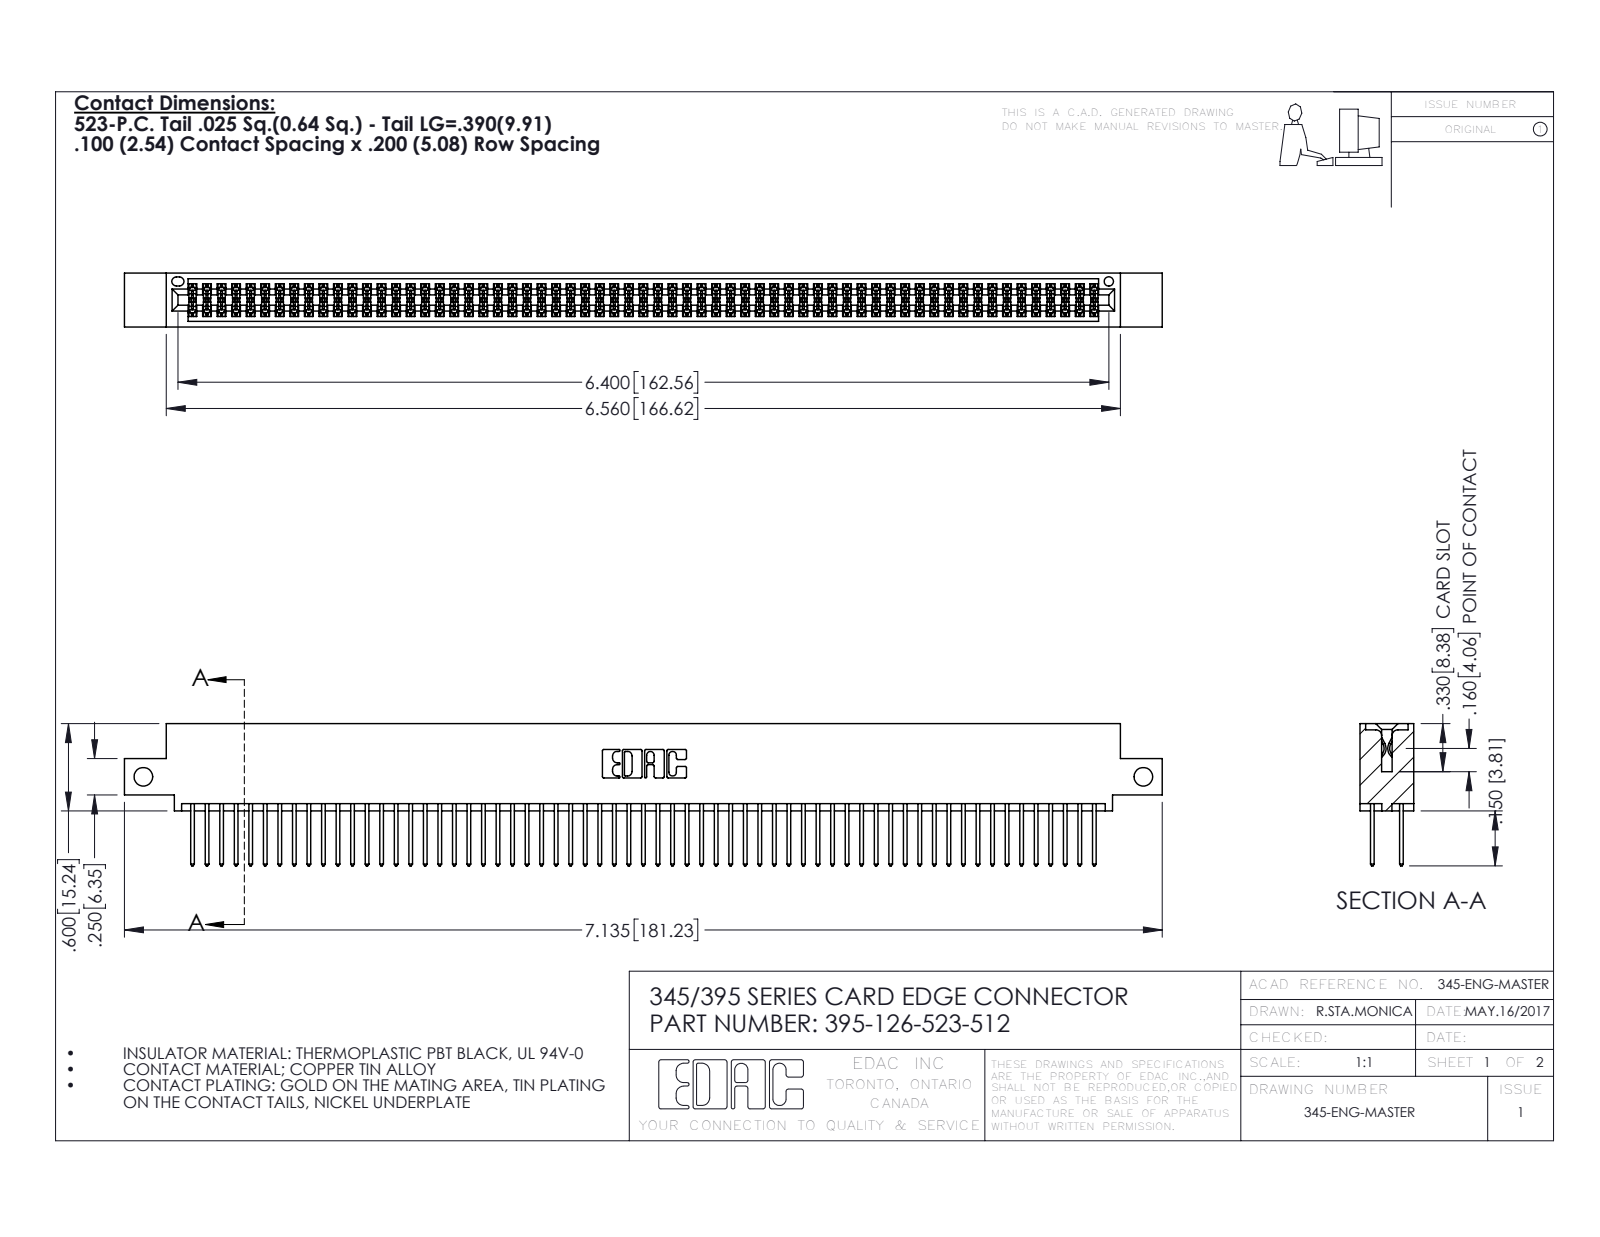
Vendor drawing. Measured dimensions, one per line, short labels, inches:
name: 345 Part_0.110 Offset - Side Mount; 345-292-001_345-293-123; 395-126-523-512
written by: SolidWorks 2016 (CONFIG_CONTROL_DESIGN)
unit: in
bodies: 127 solids, 6430 faces (4242 planar, 2188 cylindrical, 0 other)
size: 7.135 × 0.977 × 0.37
volume: 1.092 in³; area: 43.37 in²
holes: 2× ⌀0.128, 1× ⌀0.064
rounds: 189× R0.006, 126× R0.01, 22× R0.01, 6× R0.007, 6× R0.031, 3× R0.026, 2× R0.014, 2× R0.019
face distances: 0.298, 0.072, 0.2, 0.098, 0.272, 0.025, 0.37, 0.225, 0.175, 0.149
hole spacings: 6.875
